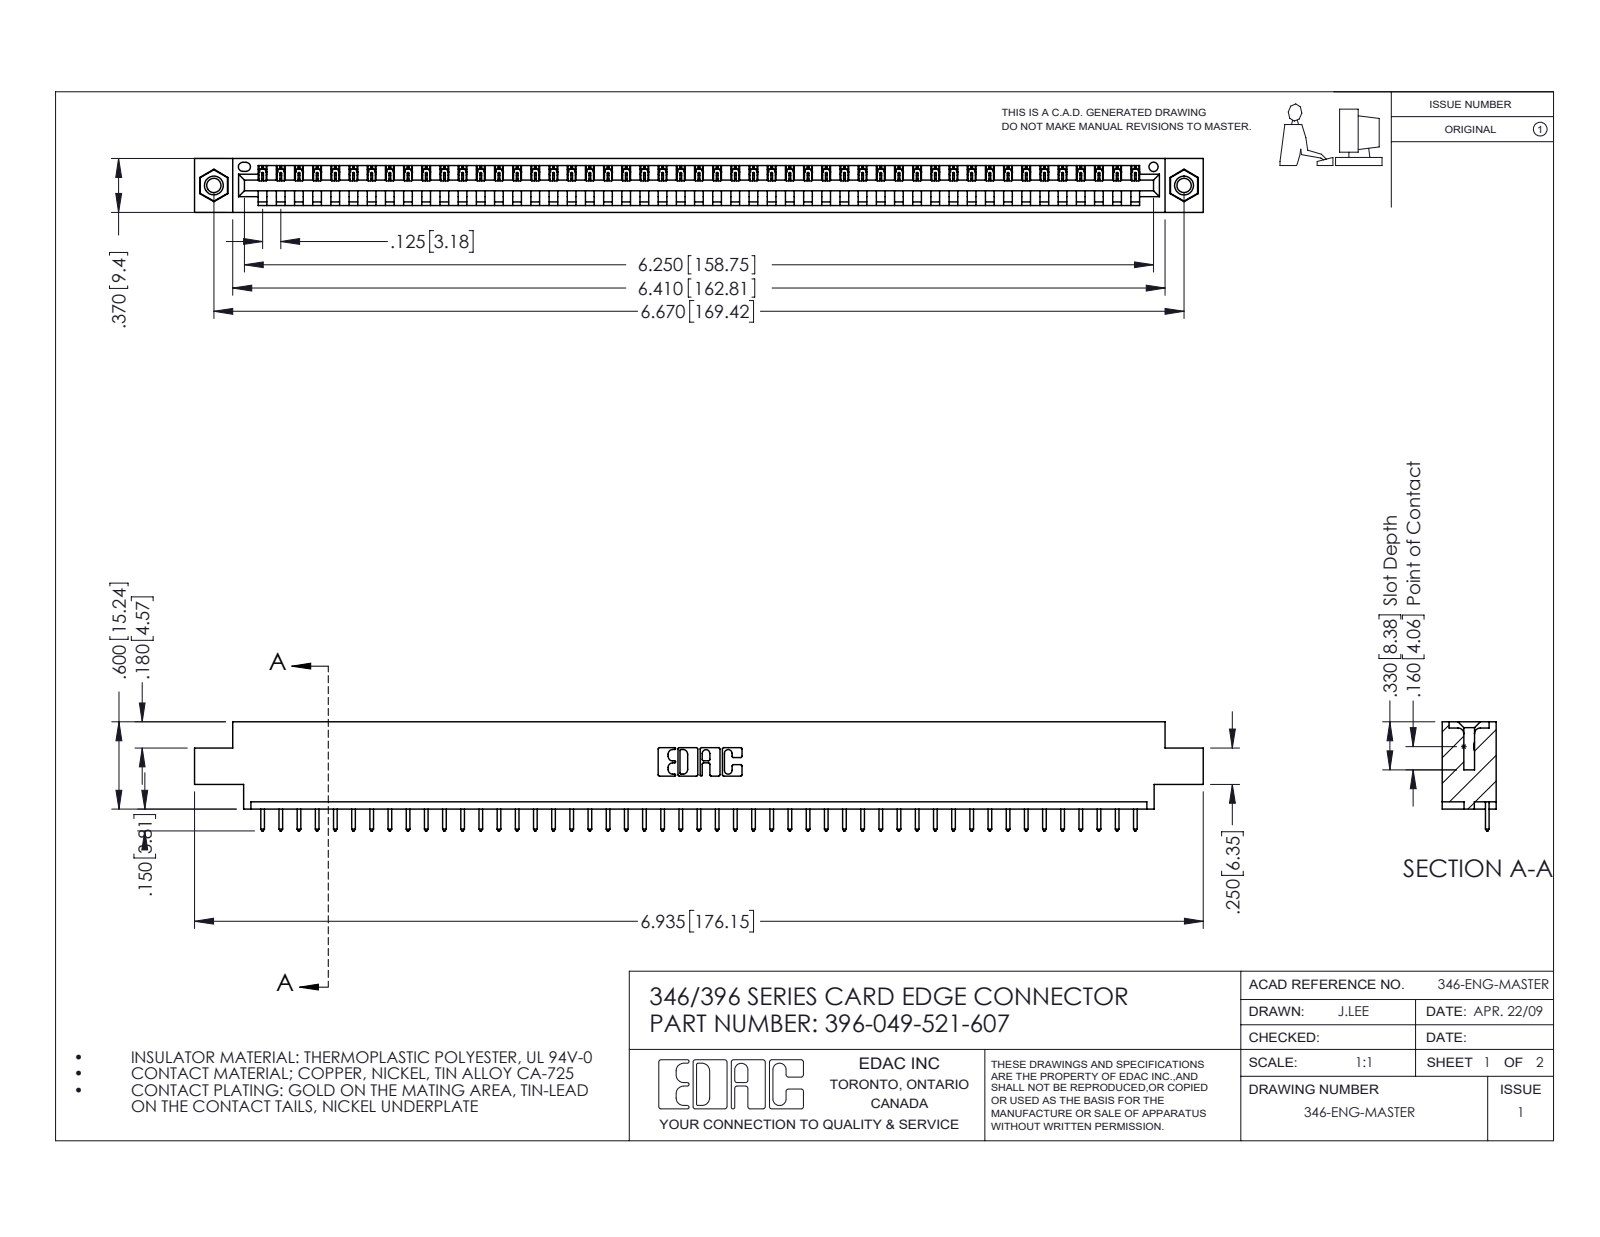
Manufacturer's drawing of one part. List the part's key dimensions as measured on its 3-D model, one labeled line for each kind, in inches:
Part name (STEP PRODUCT): 346 Part_0.170 Offset - 0.156 Dia-TI; 396-049-521-607; 345-250-001_345-250-005-103; 345-292-001_345-293-121
STEP written by: SolidWorks 2016 (CONFIG_CONTROL_DESIGN)
Units: inches
Bodies: 52 solids, 3028 faces (2072 planar, 940 cylindrical, 16 other)
Overall size (bounding box): 6.935 × 0.75 × 0.37
Volume: 1.013 in³ · Surface area: 31.72 in²
Round holes (diameter × count): ⌀0.098 ×2, ⌀0.125 ×2, ⌀0.156 ×2, ⌀0.064 ×1
Round bosses / shafts (diameter × count): ⌀0.155 ×2
Partial cylindrical surfaces — rounded edges, fillets, slot ends (radius × count): R0.006 ×98, R0.01 ×98, R0.01 ×22, R0.007 ×6, R0.031 ×6, R0.026 ×3, R0.031 ×2, R0.04 ×2
Main face-to-face distances: 0.048, 0.322, 0.37, 0.25, 0.072, 0.298, 0.025, 0.222, 0.148, 0.1
Hole centre spacings: 0.246, 6.461, 6.67
